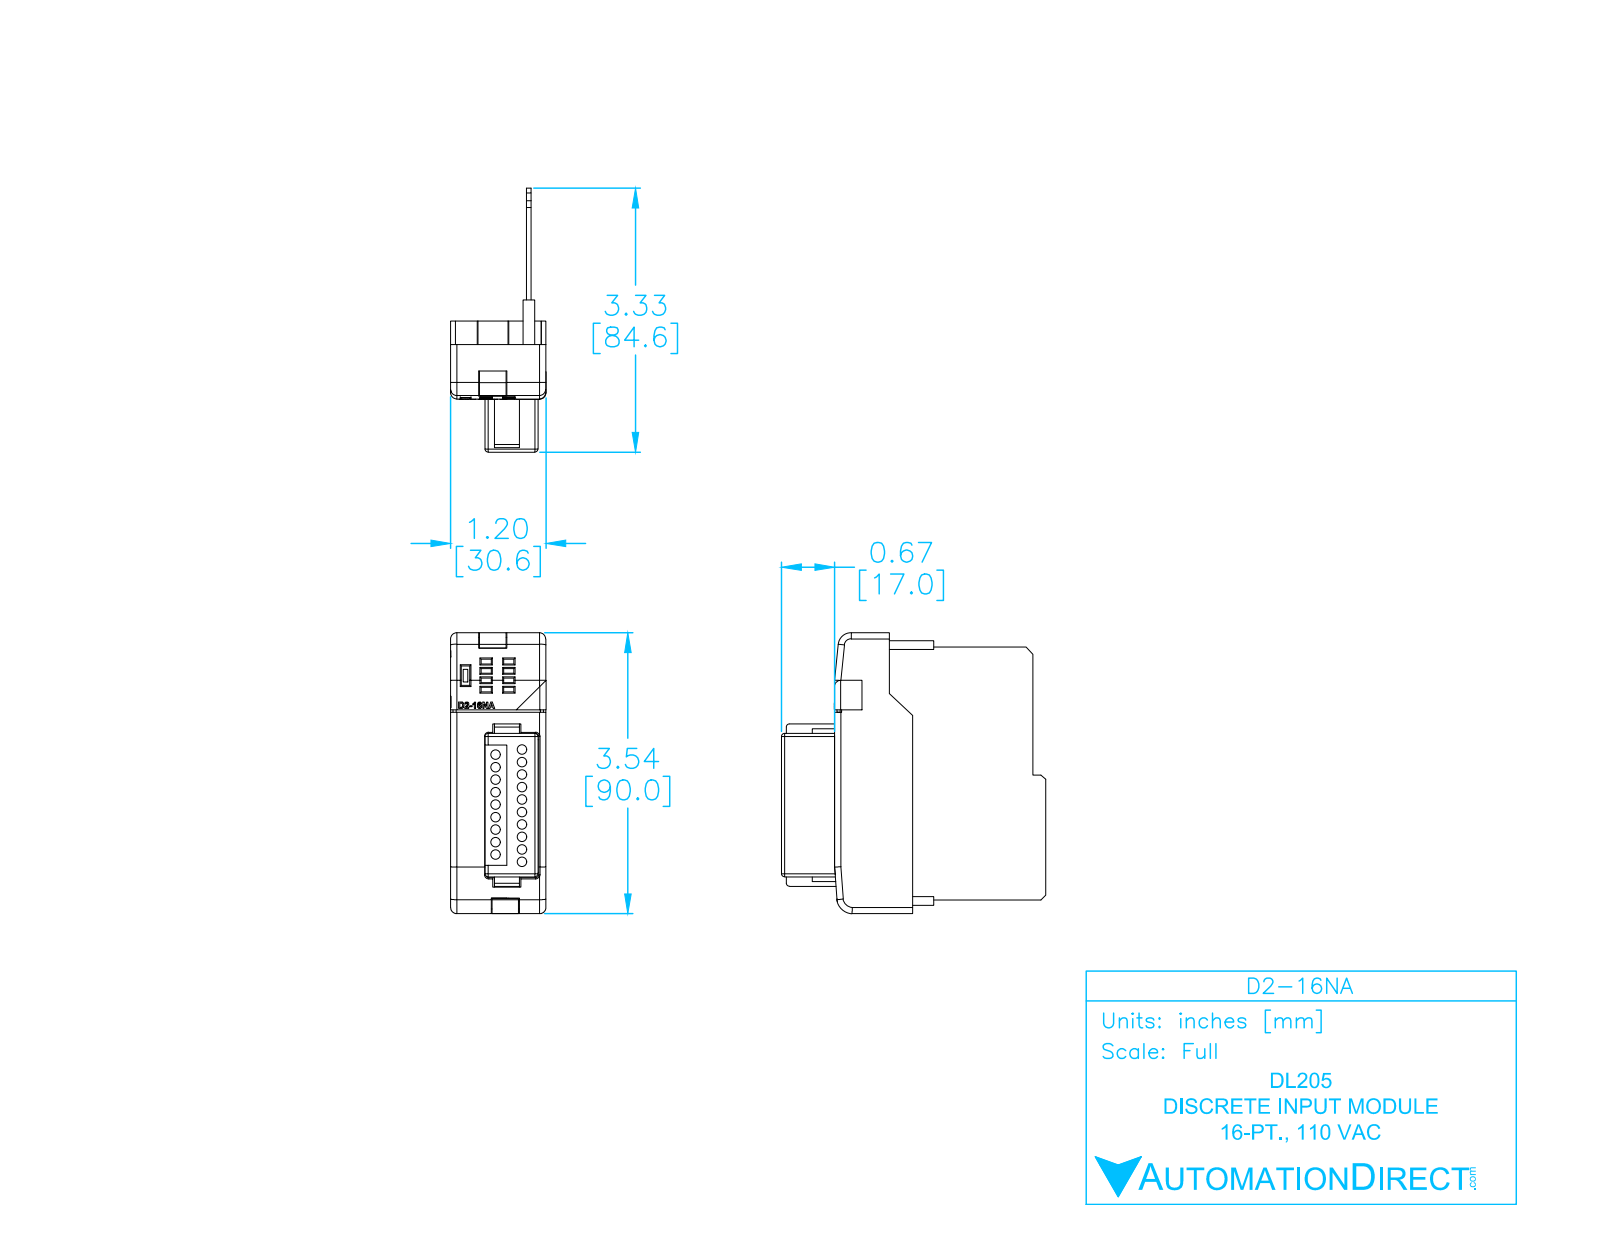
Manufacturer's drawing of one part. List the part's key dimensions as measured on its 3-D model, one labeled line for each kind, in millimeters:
Part name (STEP PRODUCT): D2-16NA_ModuleCase Light_NEW
STEP written by: SolidWorks 2009 (AUTOMOTIVE_DESIGN)
Units: millimetres
Bodies: 2 solids, 617 faces (407 planar, 158 cylindrical, 52 other)
Overall size (bounding box): 90 × 84.6 × 30.55
Volume: 30 556 mm³ · Surface area: 32 607 mm²
Round holes (diameter × count): ⌀3 ×19
Partial cylindrical surfaces — rounded edges, fillets, slot ends (radius × count): R0.35 ×28, R1 ×18, R0.5 ×12, R2 ×11, R0.25 ×6, R2.62 ×1, R3.79 ×1, R4.12 ×1
Main face-to-face distances: 1.5, 4.72, 3.22, 6.22, 0.5, 1, 24.28, 29, 18, 11
Hole centre spacings: 4, 8, 12, 16, 8.61, 8.77, 20, 10.16
